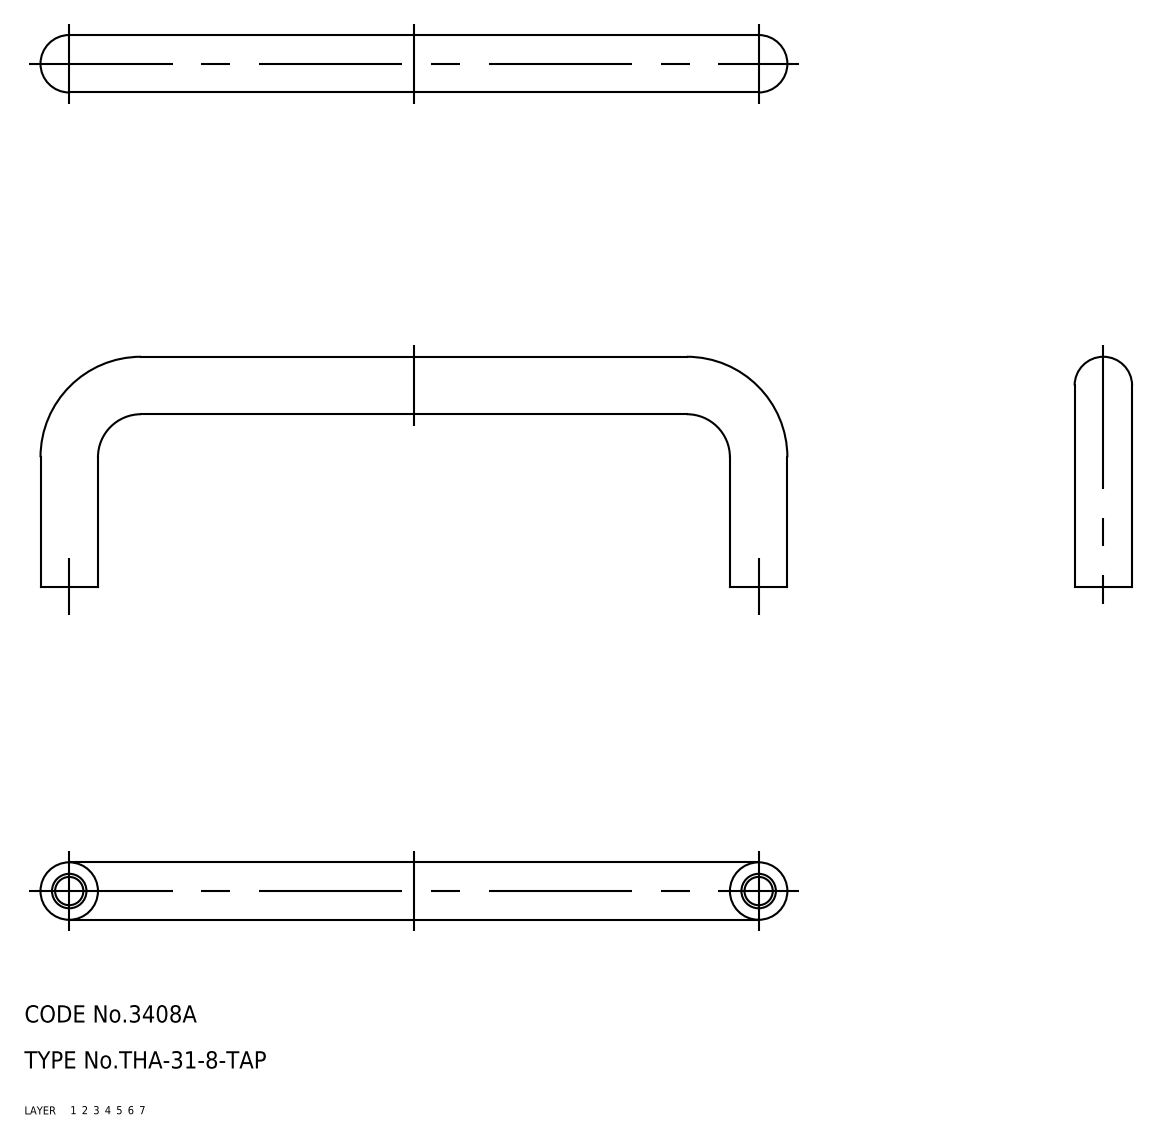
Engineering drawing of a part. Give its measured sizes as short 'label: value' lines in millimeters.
name: pull
written by: CADfix (AUTOMOTIVE_DESIGN)
unit: mm
bodies: 1 solid, 18 faces (0 planar, 0 cylindrical, 18 other)
size: 130 × 40 × 10
volume: 13 227 mm³; area: 6 396 mm²
